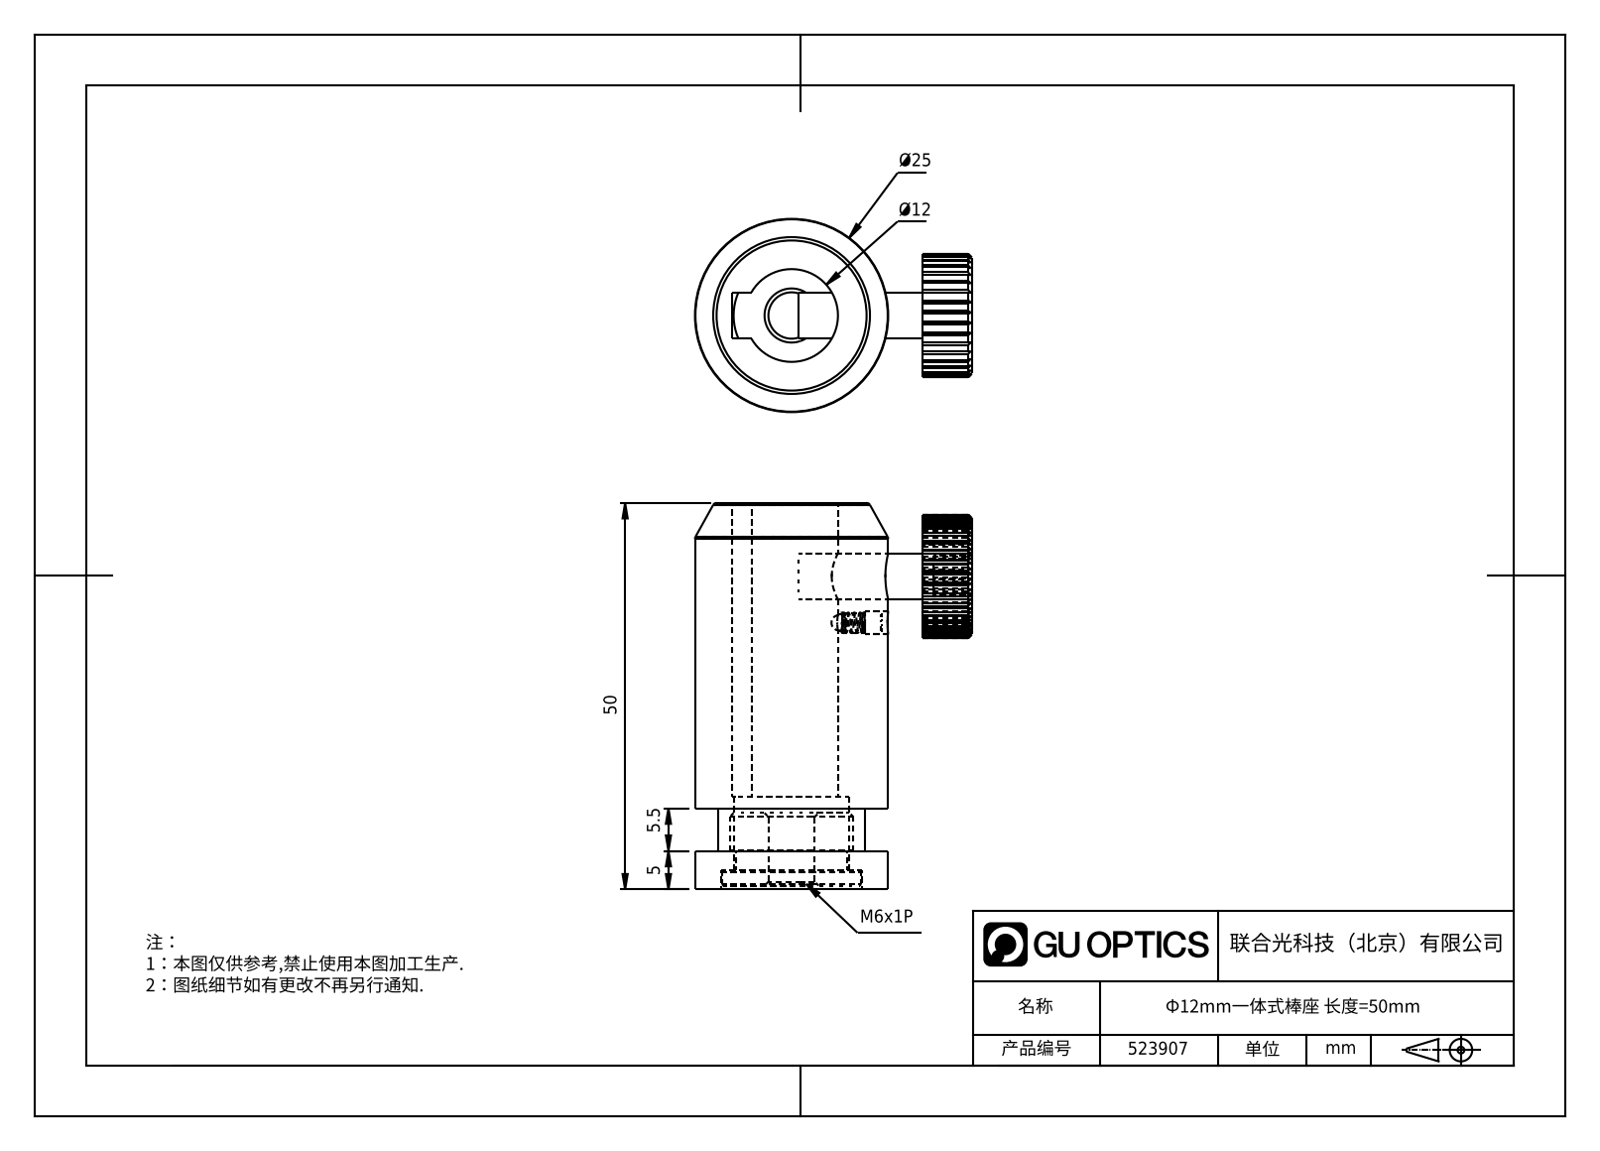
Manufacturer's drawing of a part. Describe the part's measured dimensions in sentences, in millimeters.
The part is named "M-PHF-12-50". Its 3-D file was written by "SolidWorks 2019 (CONFIG_CONTROL_DESIGN)". It is 3 solids with 217 faces: 114 planar, 81 cylindrical and 22 other. Overall it measures 50 by 35.84 by 25 millimeters. Its volume is 18 838 cubic millimeters and its surface area 8 596 square millimeters. Round holes: 1 of diameter 2.1, 1 of diameter 2.12, 1 of diameter 2.6, 1 of diameter 6, 1 of diameter 12, 1 of diameter 15, 1 of diameter 18.2. Round bosses or shafts: 1 of diameter 25, 1 of diameter 19, 1 of diameter 18, 1 of diameter 14.3, 1 of diameter 6, 1 of diameter 3, 1 of diameter 2.16, 1 of diameter 0.99. Partial cylindrical surfaces (rounded edges, fillets, slot ends): 1 of radius 8. The main face-to-face distances are 5, 10.5, 5.5, 0.5, 4.5, 10, 50, 49.5, 45, 39.5.
